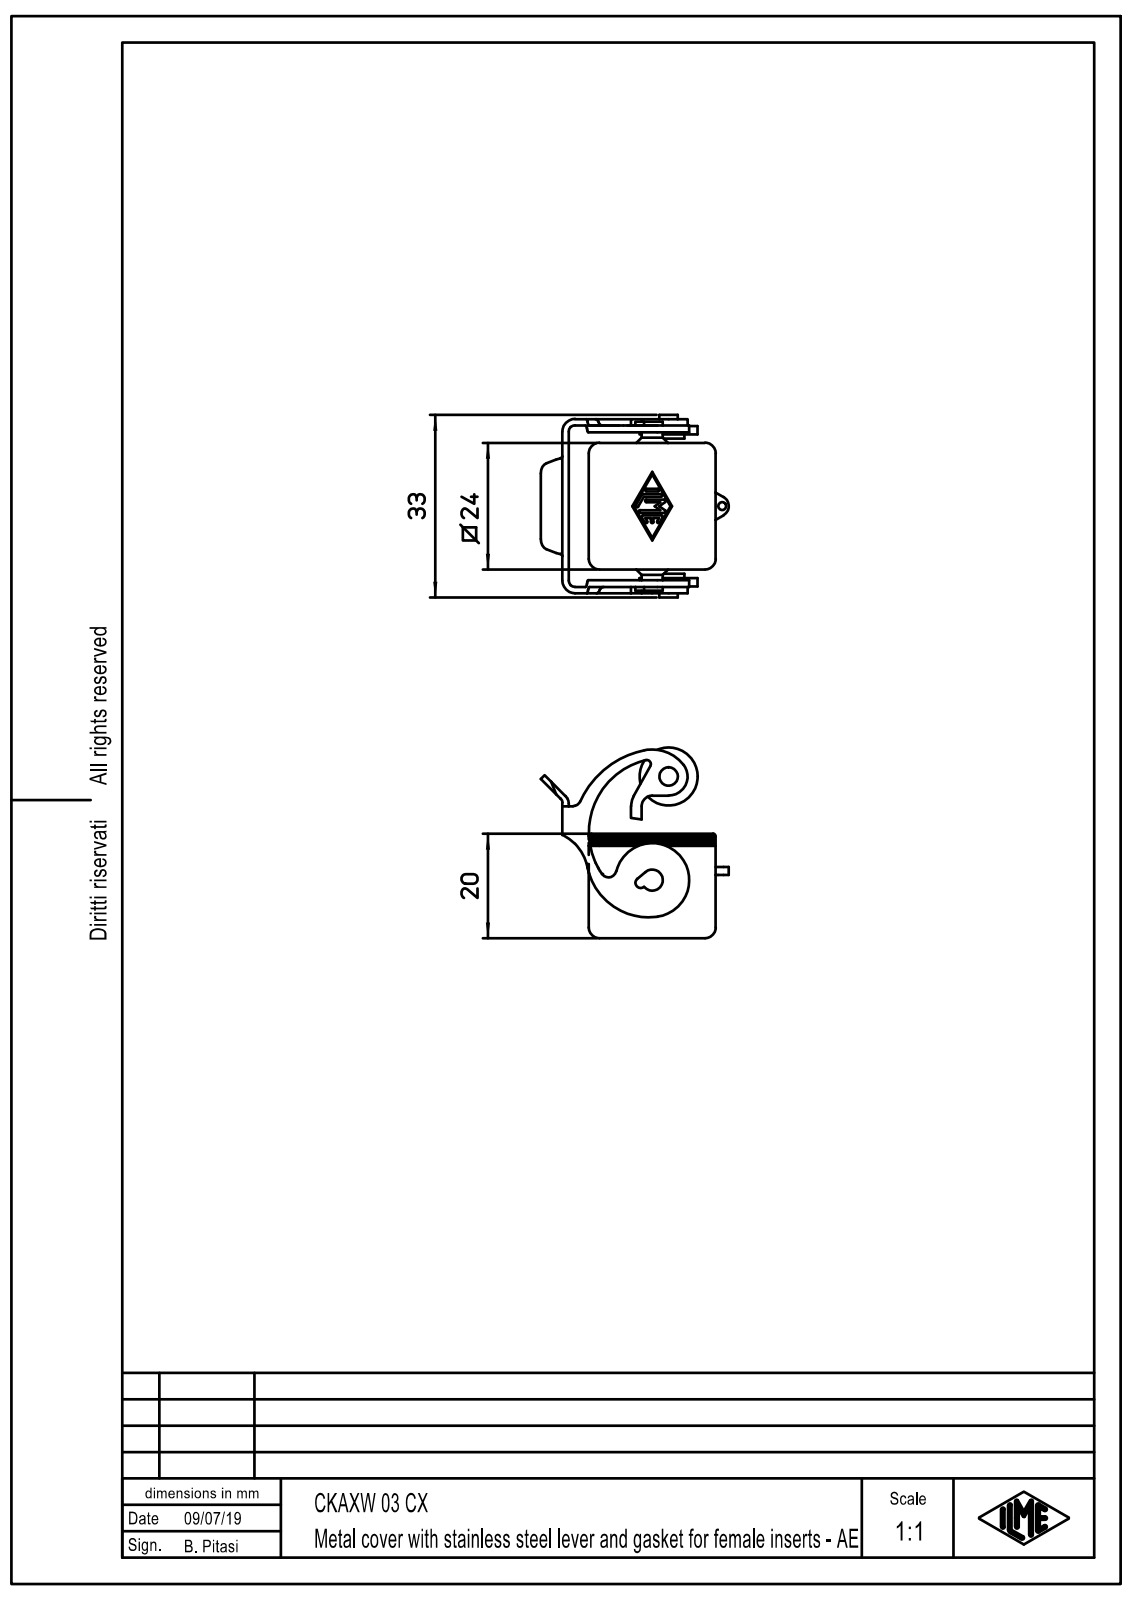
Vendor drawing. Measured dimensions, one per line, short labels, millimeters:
name: CKAXW_03_CX
written by: Creo Elements/Direct Modeling 20.1B 02-Apr-2019 (C) Parametric Technology GmbH (AUTOMOTIVE_DESIGN)
unit: mm
bodies: 1 solid, 194 faces (72 planar, 106 cylindrical, 16 other)
size: 36.1 × 35.57 × 34.6
volume: 5 044 mm³; area: 7 245 mm²
holes: 1× ⌀1.5
bosses: 1× ⌀11, 1× ⌀6, 1× ⌀4, 1× ⌀3.5, 1× ⌀3.2
rounds: 15× R2, 12× R0.5, 10× R1.2, 2× R1, 2× R1.5, 2× R2.4, 1× R0.75, 1× R3.6
face distances: 1.5, 22.5, 2, 21, 24, 1.2, 3.3, 4.8, 25.8, 27.3
